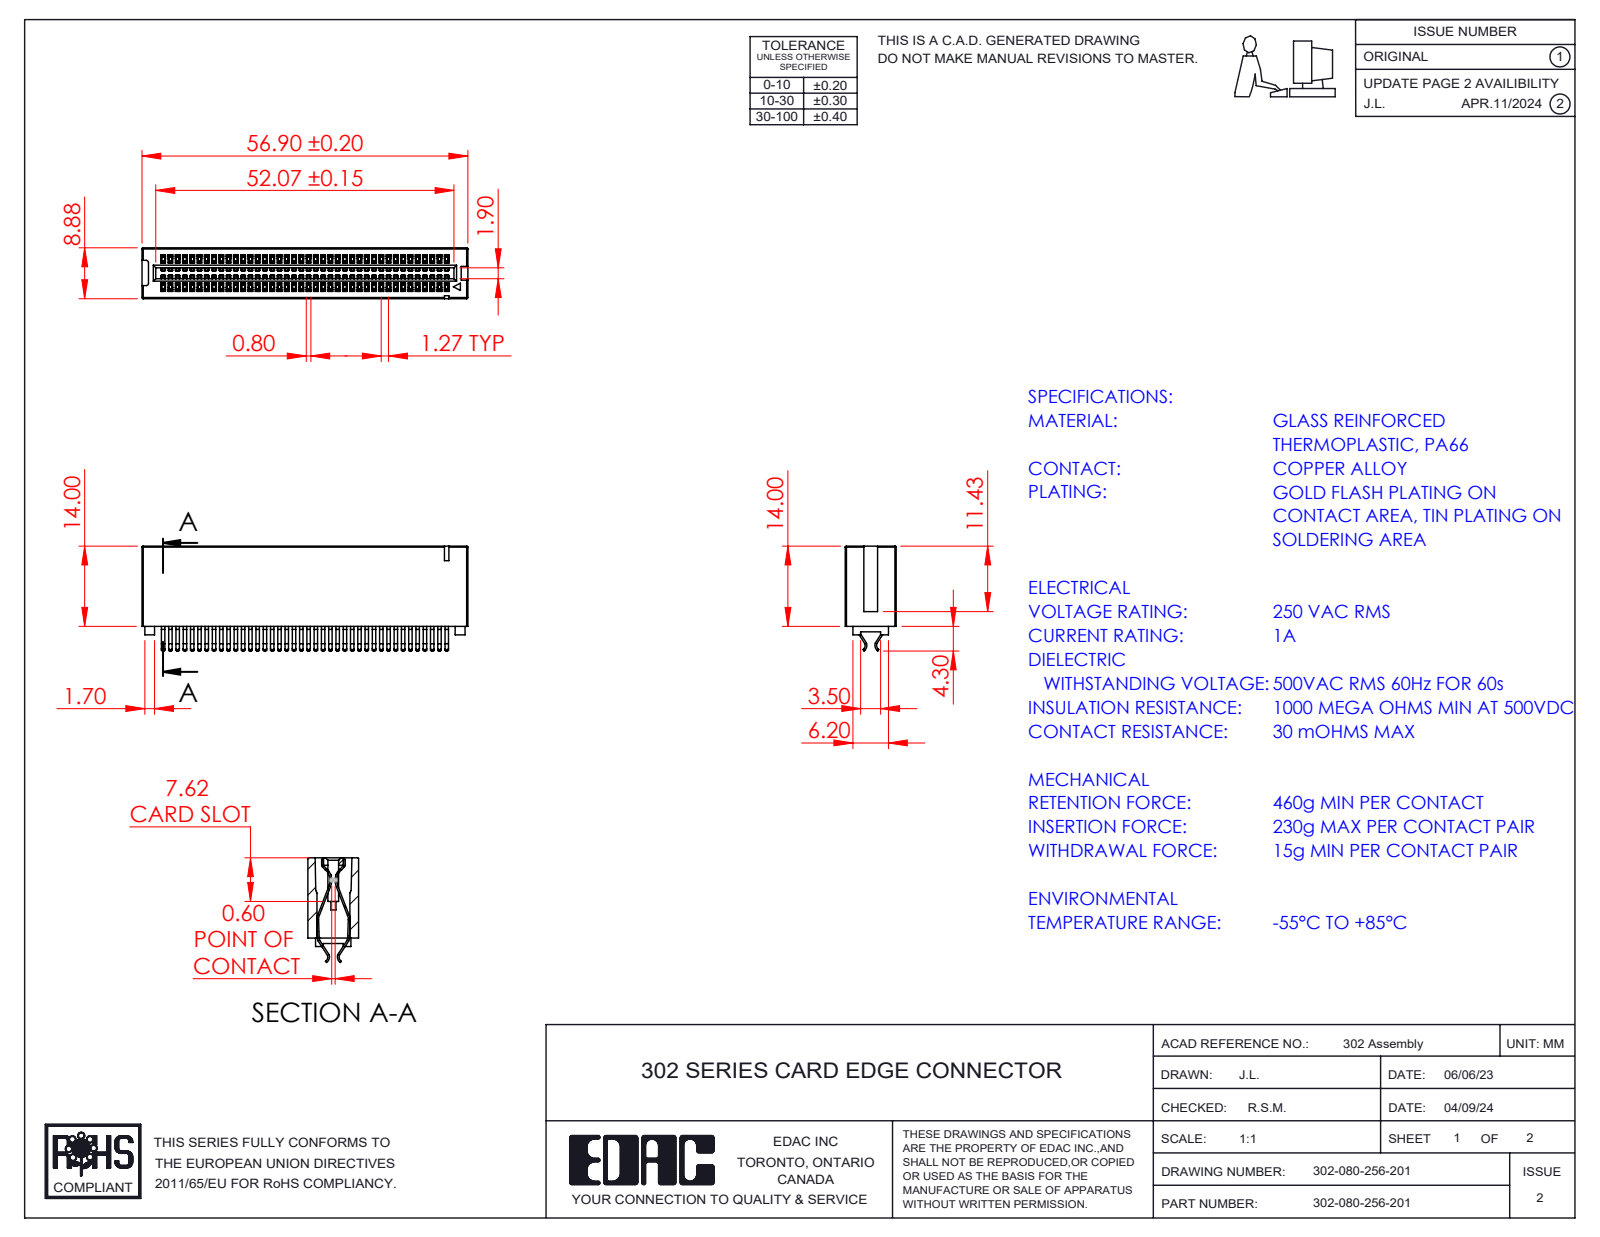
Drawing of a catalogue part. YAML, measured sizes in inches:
part_name: "HSG_Vertical HSG; Contact_302-290-X56; 302-080-256-201"
step_written_by: "SolidWorks 2023 (CONFIG_CONTROL_DESIGN)"
units: inches
bodies: {solids: 81, faces: 3866, planar: 2569, cylindrical: 1293, other: 4}
overall_size: [2.24, 0.72, 0.35]
volume: 0.269
surface_area: 19.08
partial_cylinders:
  - {radius: 0.008, count: 248}
  - {radius: 0.004, count: 2}
  - {radius: 0.016, count: 2}
  - {radius: 0.016, count: 2}
  - {radius: 0.037, count: 2}
  - {radius: 0.041, count: 2}
  - {radius: 0.048, count: 2}
  - {radius: 0.049, count: 2}
face_to_face_distances: [0.05, 0.1, 0.15, 0.2, 0.3, 0.25, 0.35, 0.35, 0.4, 0.45]
